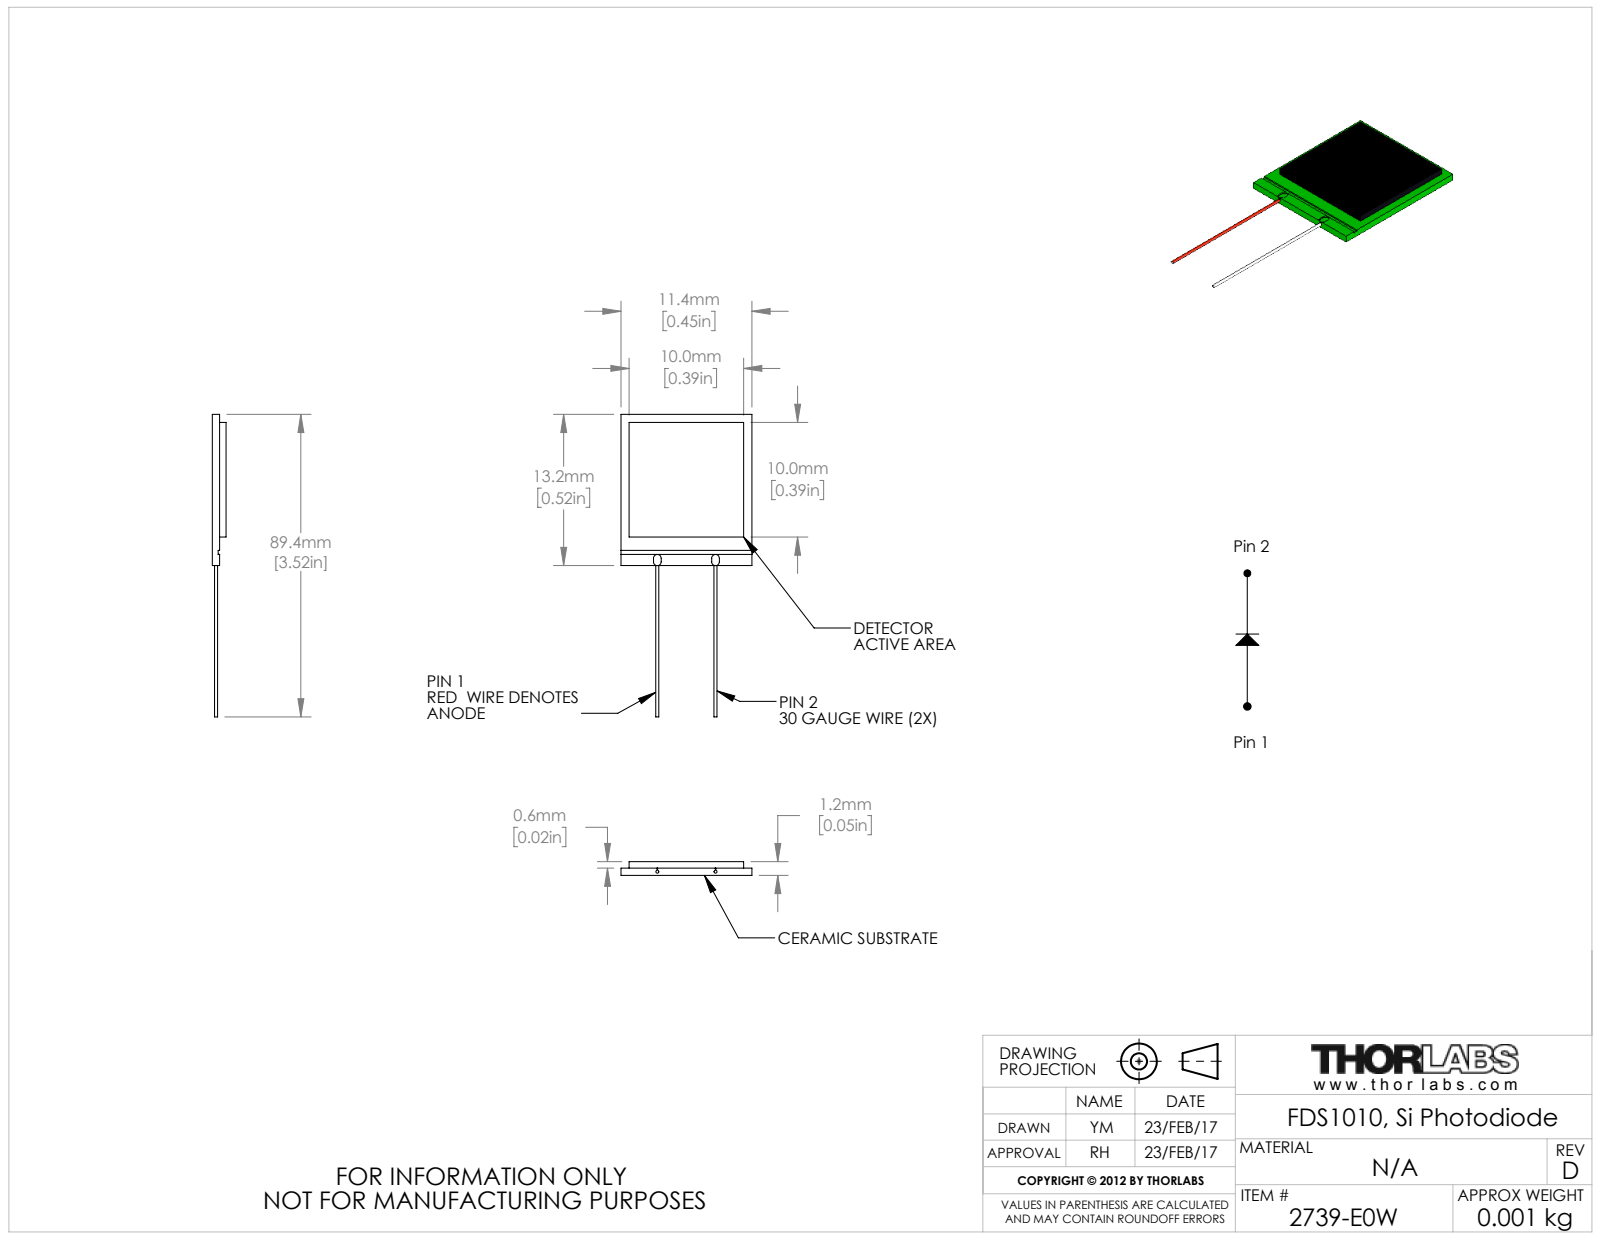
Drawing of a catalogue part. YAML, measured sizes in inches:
part_name: "2739-E0W"
step_written_by: "SolidWorks 2018 (AUTOMOTIVE_DESIGN)"
units: inches
bodies: {solids: 3, faces: 41, planar: 27, cylindrical: 14, other: 0}
overall_size: [1.04, 0.45, 0.047]
volume: 0.009
surface_area: 0.59
round_bosses_or_shafts:
  - {diameter: 0.01, count: 2}
partial_cylinders:
  - {radius: 0.013, count: 4}
face_to_face_distances: [0.047, 0.025, 0.022, 0.028, 0.422, 0.394, 0.45, 0.52, 0.098, 0.492]
